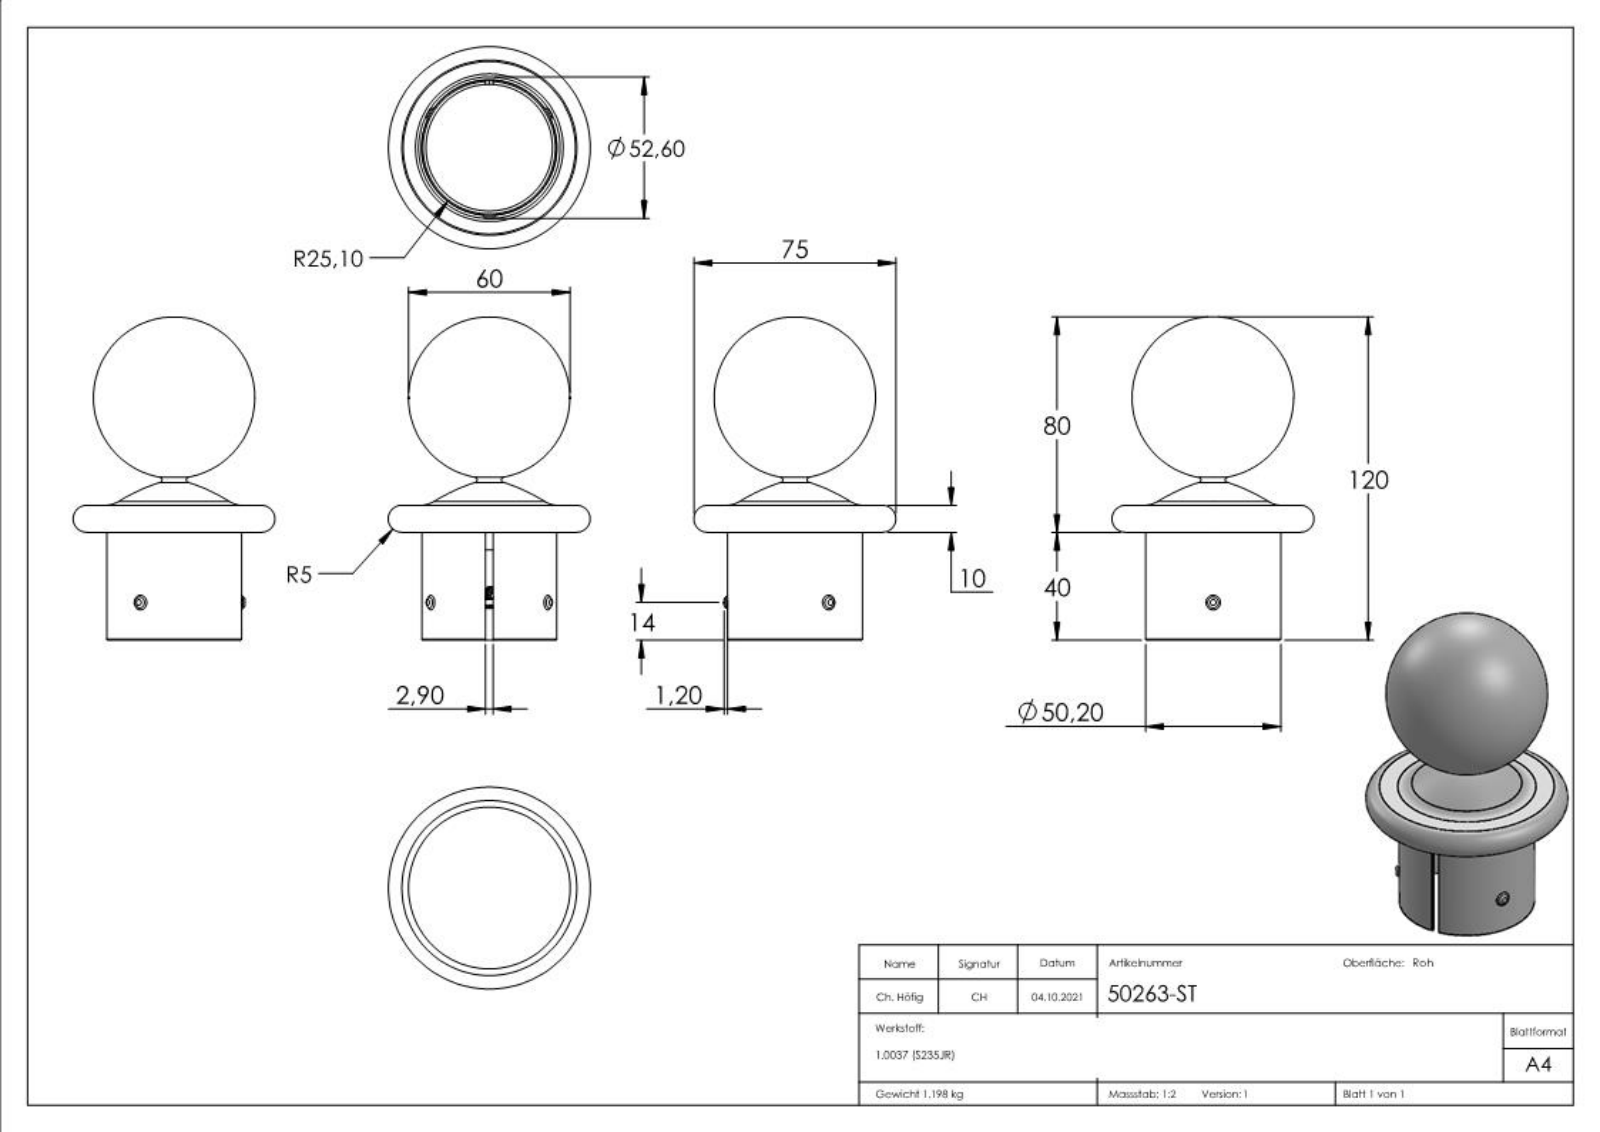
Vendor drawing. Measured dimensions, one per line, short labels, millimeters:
name: 50263-ST
written by: SolidWorks 2018 (CONFIG_CONTROL_DESIGN)
unit: mm
bodies: 1 solid, 289 faces (117 planar, 28 cylindrical, 144 other)
size: 120 × 75 × 75
volume: 153 637 mm³; area: 35 160 mm²
holes: 1× ⌀47, 1× ⌀50.2
rounds: 1× R1.45, 1× R23.6
face distances: 7, 43, 50, 40, 3, 10, 2.9, 2.7, 2.02, 2.46
